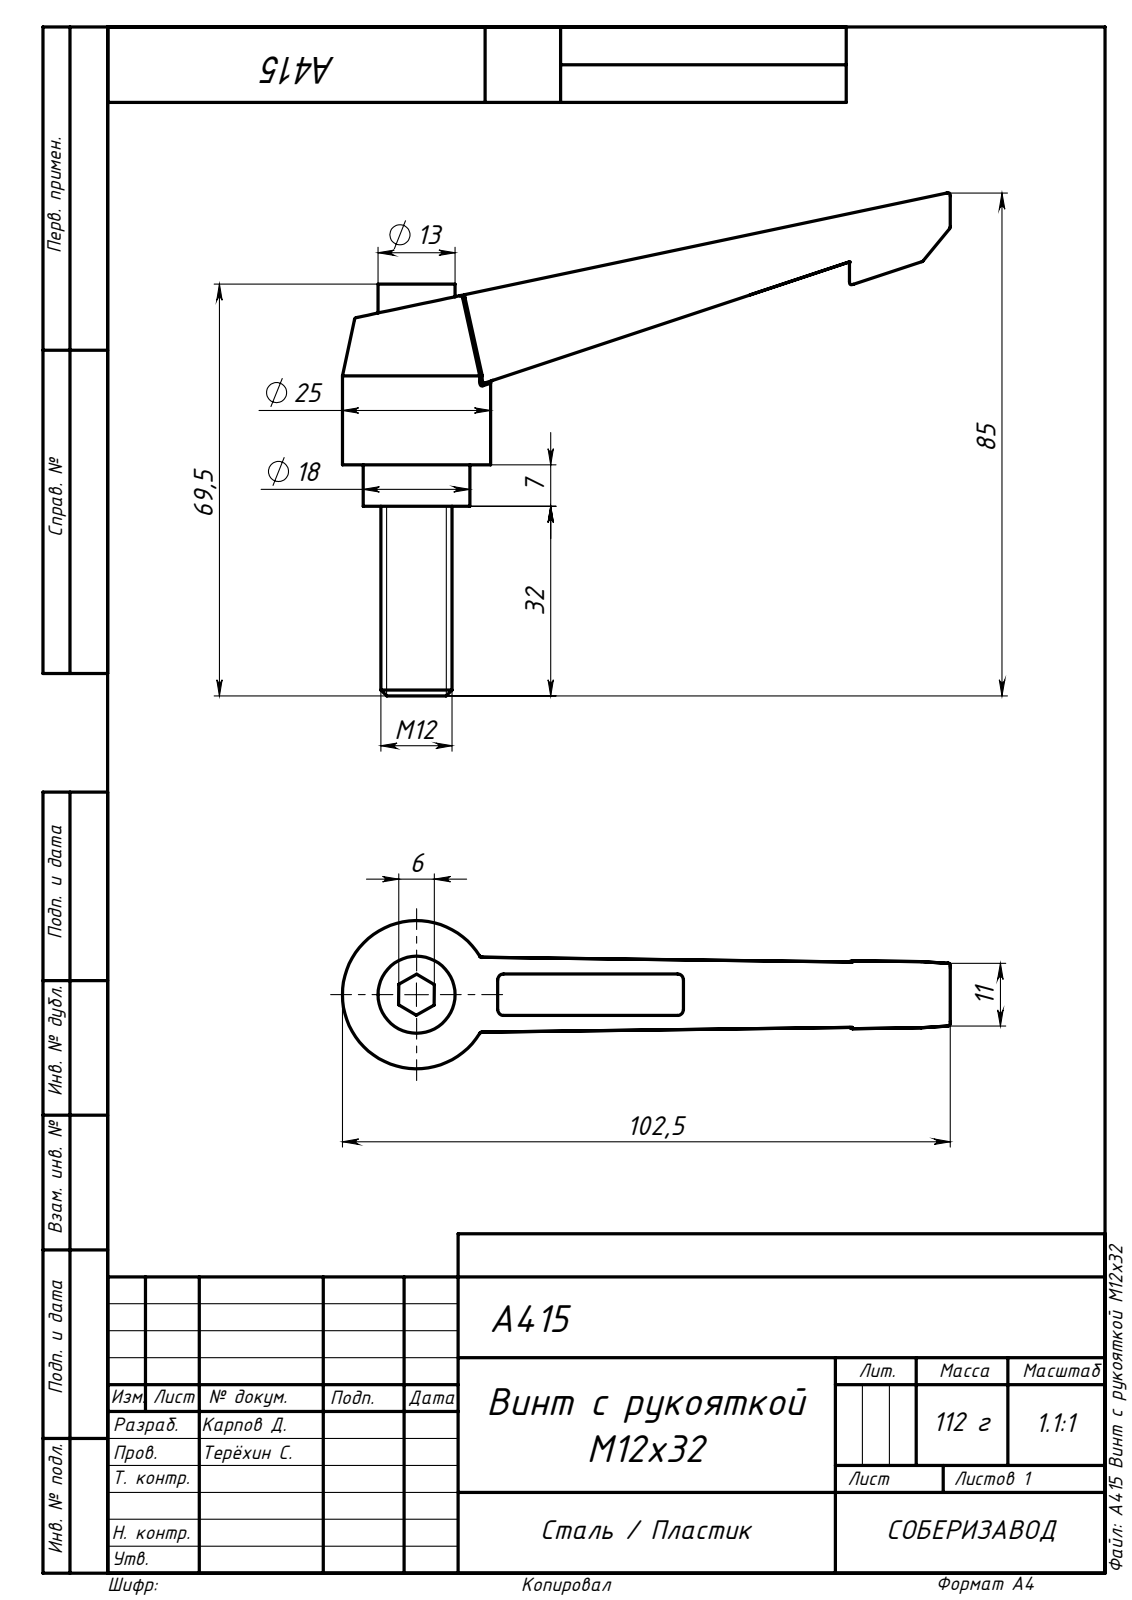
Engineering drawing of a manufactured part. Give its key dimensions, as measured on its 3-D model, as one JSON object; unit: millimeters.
{"part_name": "A415 Винт с рукояткой М12х32", "step_written_by": "SolidWorks 2020 (AUTOMOTIVE_DESIGN)", "units": "millimeters", "bodies": {"solids": 1, "faces": 81, "planar": 31, "cylindrical": 12, "other": 38}, "overall_size": [102.52, 84.9, 25], "volume_mm3": 24666, "surface_area_mm2": 9044, "round_bosses_or_shafts": [[25, 1], [18, 1], [13, 1], [12, 1]], "partial_cylinders_radius": [[1, 4]], "face_to_face_distances": [7, 8.79, 37.5, 30.5, 32, 39, 69.5, 65.44, 17, 66.5]}
